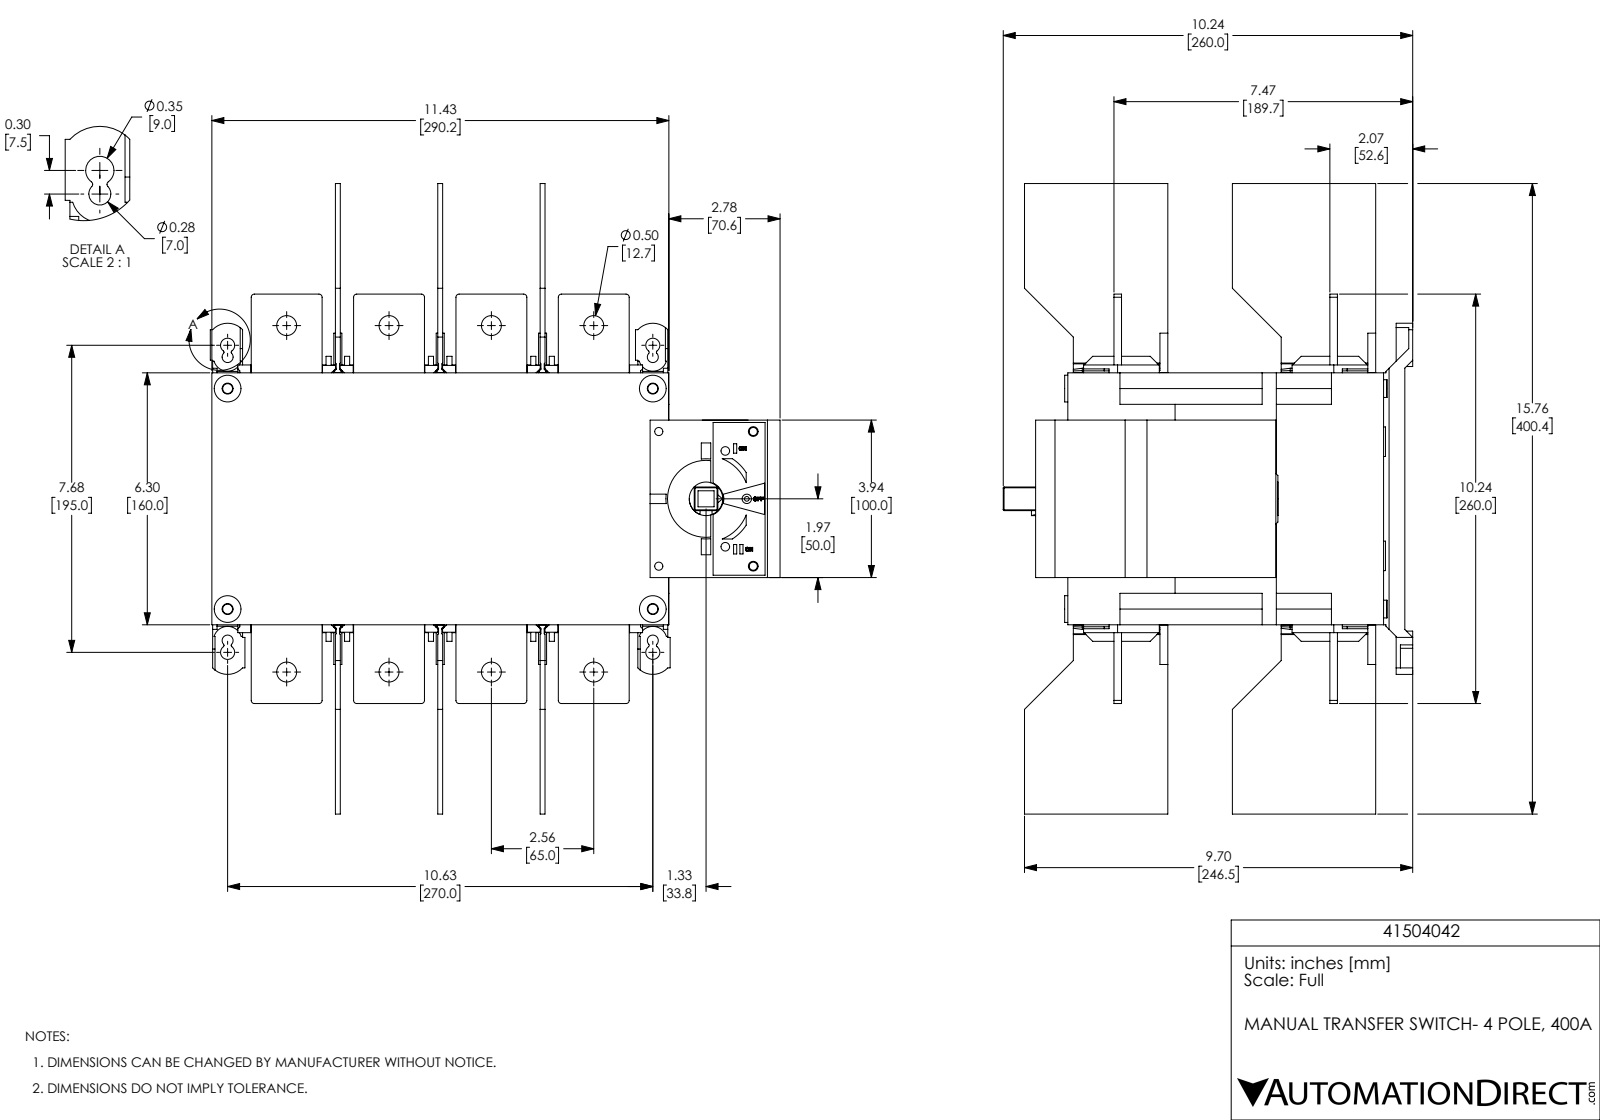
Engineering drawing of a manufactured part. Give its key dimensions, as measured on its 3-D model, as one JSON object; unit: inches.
{"part_name": "41504042", "step_written_by": "SolidWorks 2017 (AUTOMOTIVE_DESIGN)", "units": "inches", "bodies": {"solids": 15, "faces": 1717, "planar": 1427, "cylindrical": 284, "other": 6}, "overall_size": [15.764, 14.244, 10.236], "volume_in3": 620.2, "surface_area_in2": 1253, "round_holes": [[0.248, 12], [0.5, 8], [0.205, 4], [0.276, 4], [0.354, 4], [0.472, 4], [0.217, 2], [0.118, 1], [0.846, 1]], "round_bosses_or_shafts": [[0.669, 4], [0.841, 1], [0.236, 1]], "partial_cylinders_radius": [[0.079, 16], [0.344, 12], [0.039, 8], [0.217, 8], [0.049, 4], [0.138, 4], [0.236, 4], [0.354, 4]], "face_to_face_distances": [2.559, 0.122, 5.118, 2.681, 2.437, 6.299, 3.089, 3.211, 5.648, 5.77], "hole_center_spacings": [2.559, 5.118, 9.031, 10.63, 10.933, 1.083, 1.476, 1.556]}
